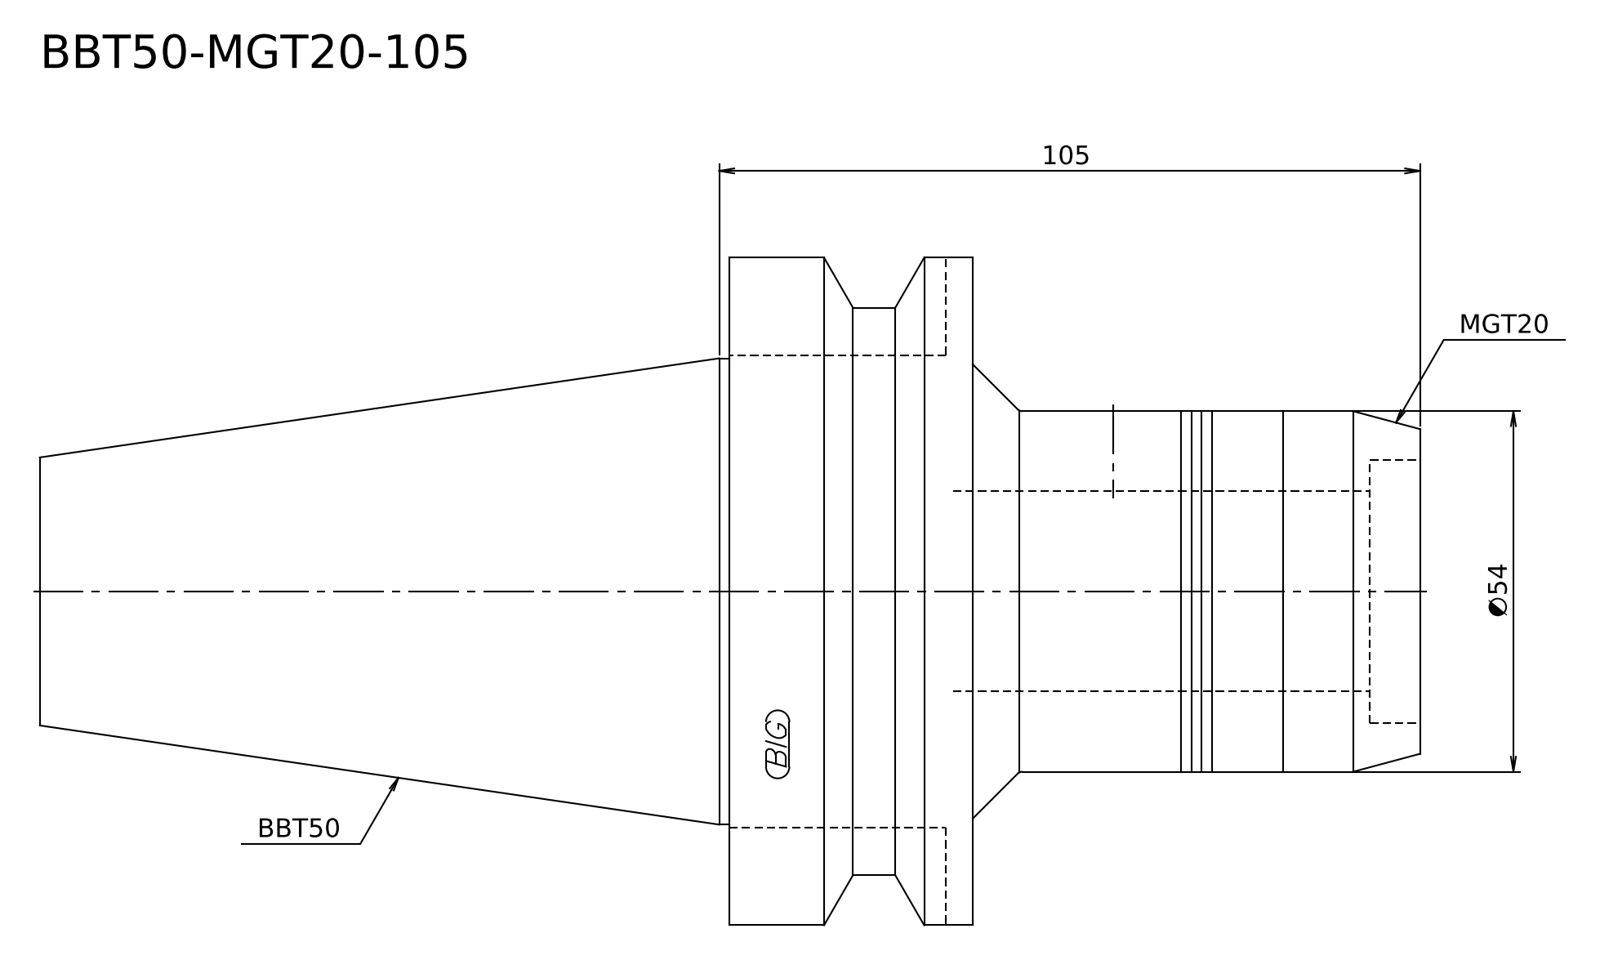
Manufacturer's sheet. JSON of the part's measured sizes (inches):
{"step_written_by": "Kubotek KeyCreator V8.5.1 (14335) (CONFIG_CONTROL_DESIGN)", "units": "inches", "bodies": {"solids": 1, "faces": 14, "planar": 4, "cylindrical": 5, "other": 5}, "overall_size": [8.142, 3.937, 3.937], "volume_in3": 41.03, "surface_area_in2": 85.26, "round_bosses_or_shafts": [[3.937, 1], [3.346, 1], [2.75, 1], [2.126, 1]], "face_to_face_distances": [1.437, 2.638, 4.075, 8.142, 5.504, 4.067]}
